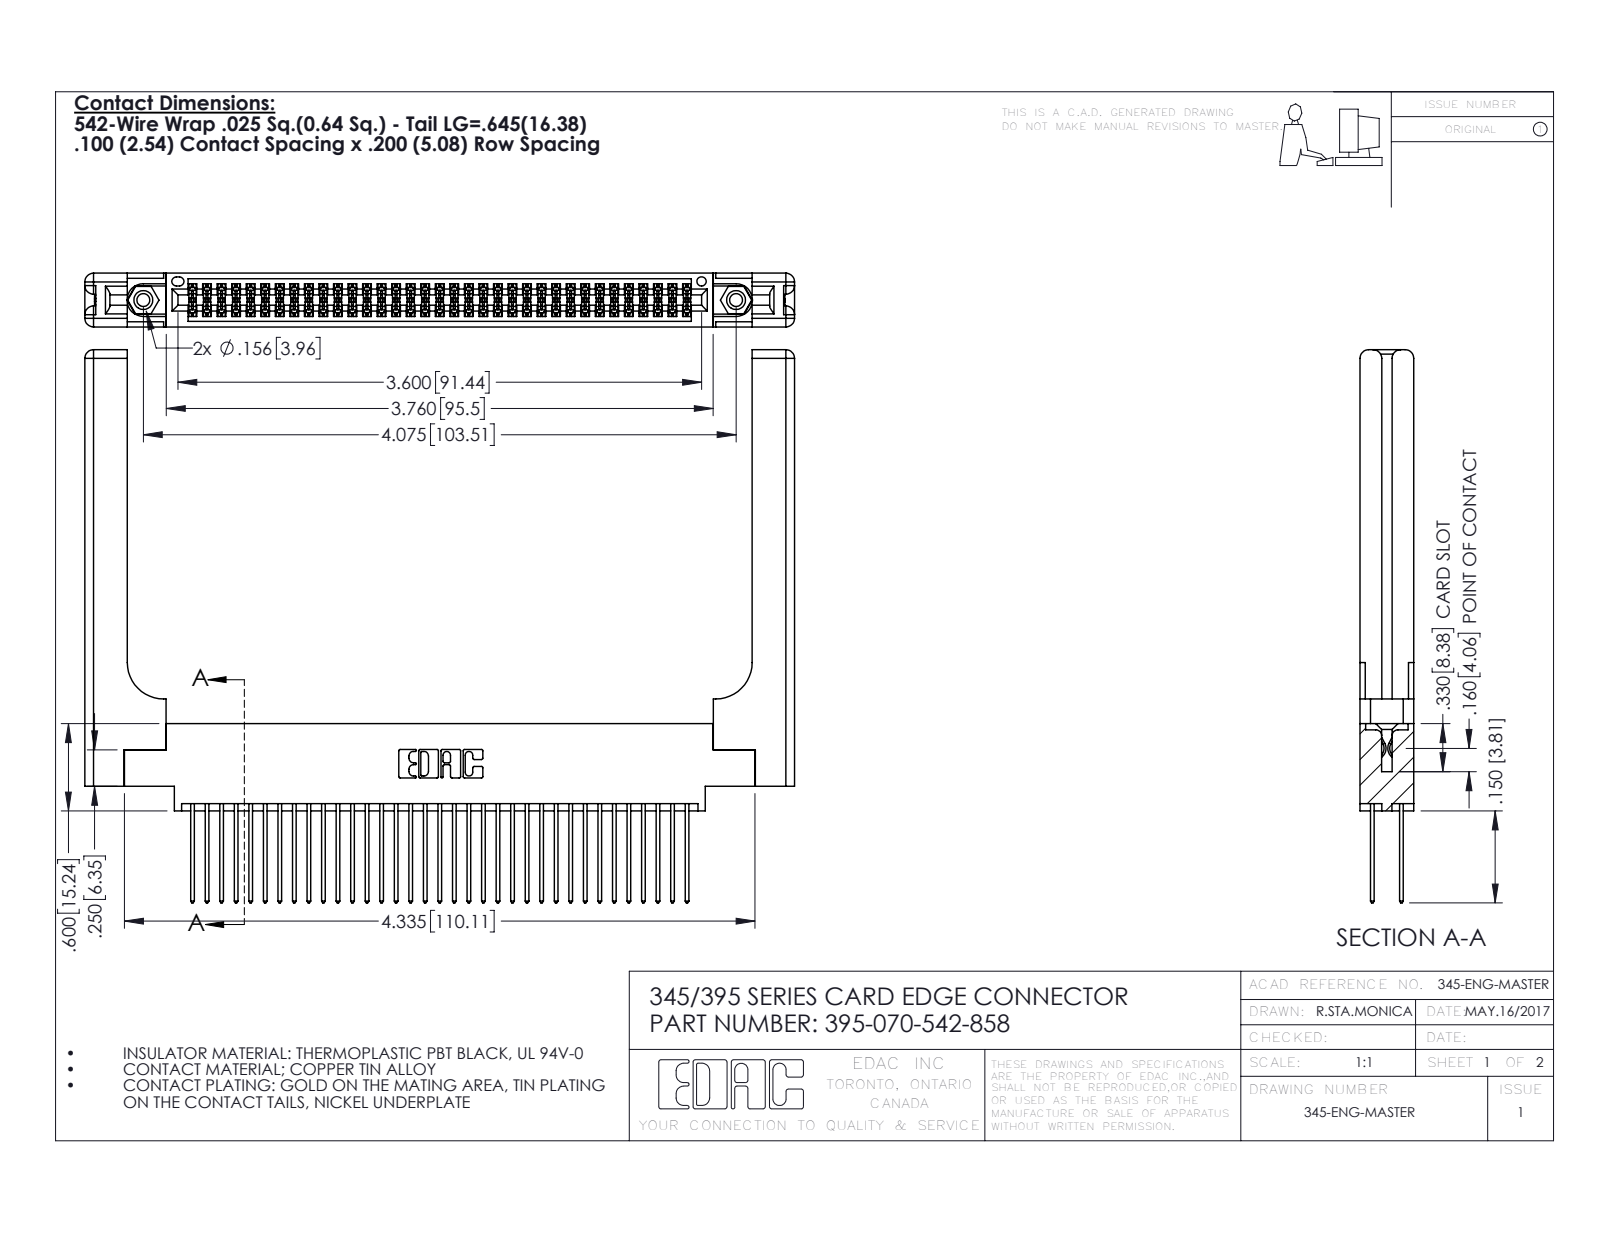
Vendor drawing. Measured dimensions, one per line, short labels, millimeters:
name: 345-250-001_345-250-001-102; 345 Part_0.170 Offset - 0.156 Dia-TH; 395-070-542-858; 345-292-001_345-293-142 (+1 more)
written by: SolidWorks 2016 (CONFIG_CONTROL_DESIGN)
unit: mm
bodies: 75 solids, 3886 faces (2542 planar, 1284 cylindrical, 60 other)
size: 123.9 × 96.6 × 9.4
volume: 20 660 mm³; area: 24 610 mm²
holes: 2× ⌀2.3, 2× ⌀3.2, 2× ⌀4, 1× ⌀1.6
bosses: 2× ⌀3.9
rounds: 105× R0.2, 70× R0.3, 22× R0.3, 16× R1.5, 6× R0.2, 6× R0.8, 3× R0.7, 2× R0.4
face distances: 1.8, 7.6, 9.4, 2.5, 6.9, 0.6, 5.1, 5.7, 4.4, 3.8
hole spacings: 6.9, 97.5, 103.5
